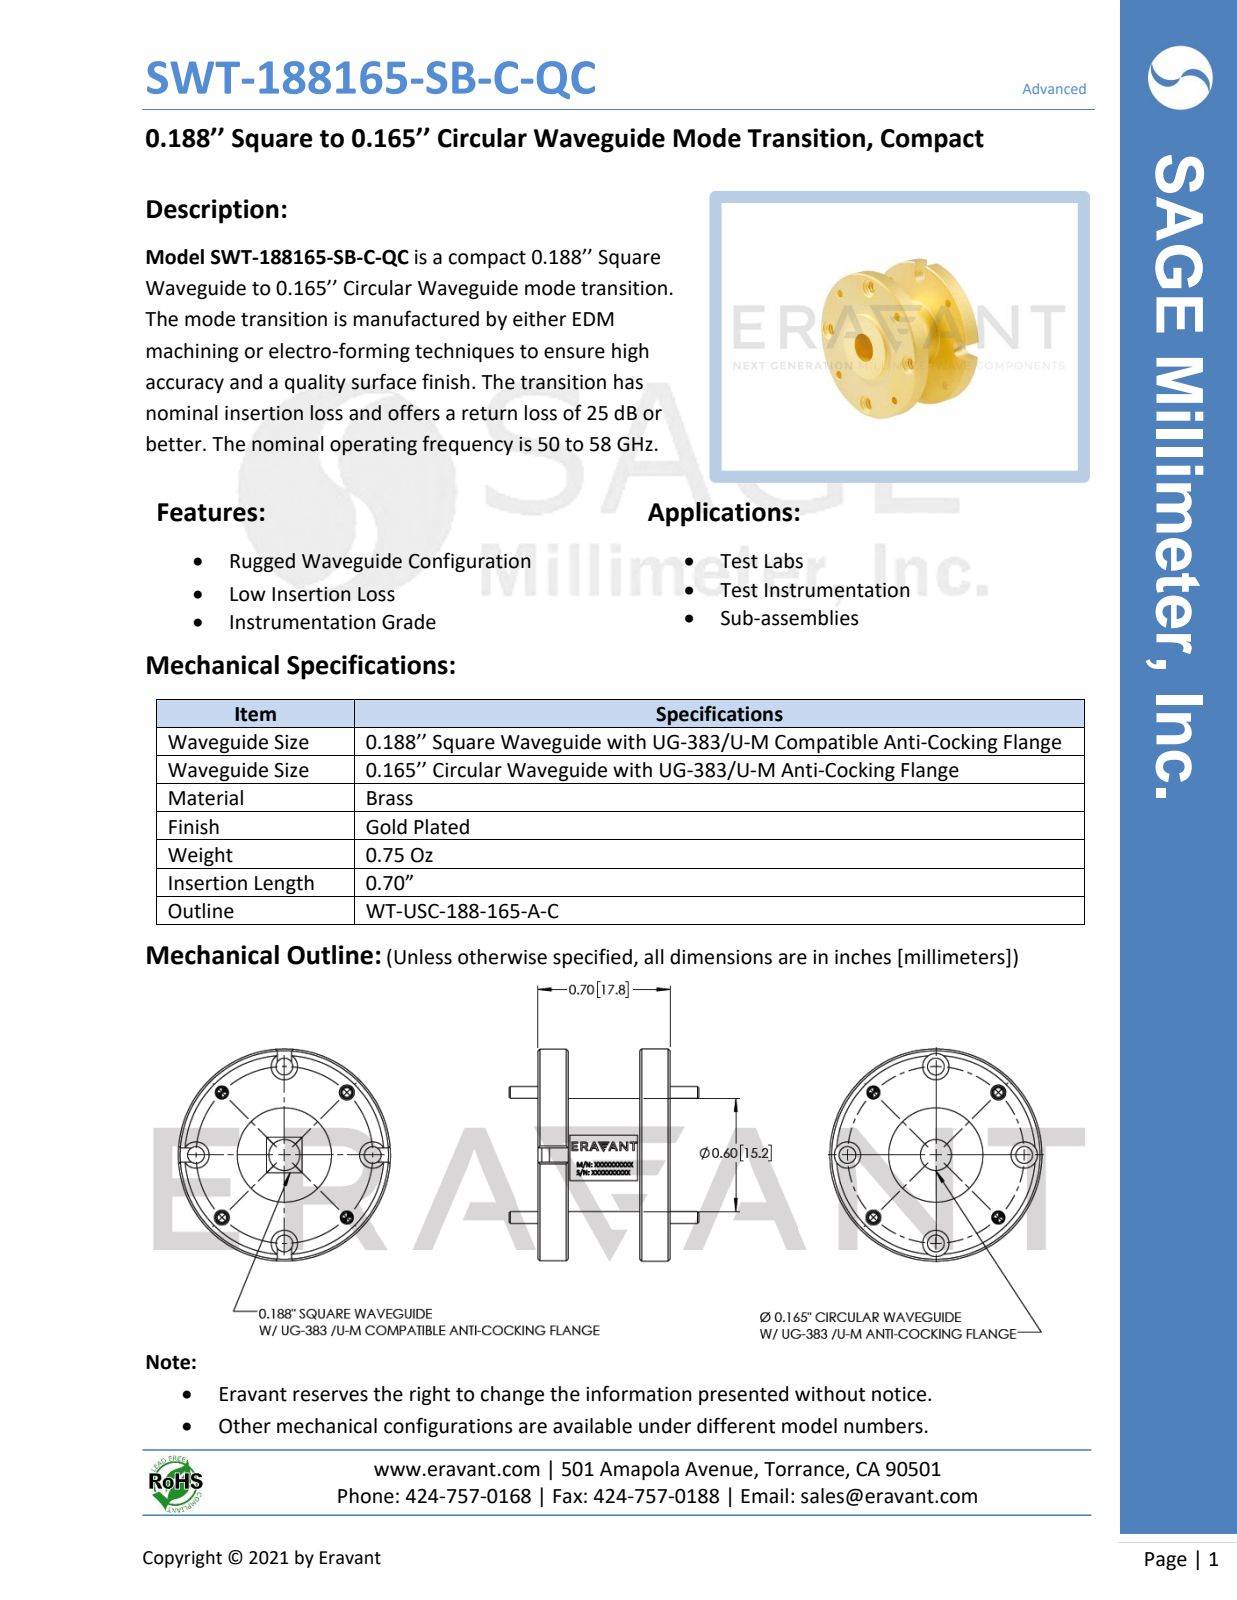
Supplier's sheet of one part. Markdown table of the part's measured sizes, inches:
| quantity | value |
| --- | --- |
| part name | WT-USC-188-165-A-C, Defeatured |
| STEP written by | SolidWorks 2021 (AUTOMOTIVE_DESIGN) |
| units | inches |
| bodies | 5 solids, 175 faces (45 planar, 78 cylindrical, 52 other) |
| overall size | 1.125 × 1.125 × 1.005 |
| volume | 0.385 in³ |
| surface area | 5.999 in² |
| round holes (diameter × count) | 0.061 × 4, 0.067 × 4, 0.089 × 4, 0.14 × 4, 1.055 × 1 |
| round bosses / shafts (diameter × count) | 0.063 × 4, 1.125 × 1, 0.6 × 1, 0.5 × 1 |
| main face-to-face distances | 0.14, 0.52, 0.38, 0.66, 0.02, 0.16, 0.54, 0.68, 0.7, 0.06 |
| hole center spacings | 0.359, 0.469, 0.663, 0.866, 0.938 |
